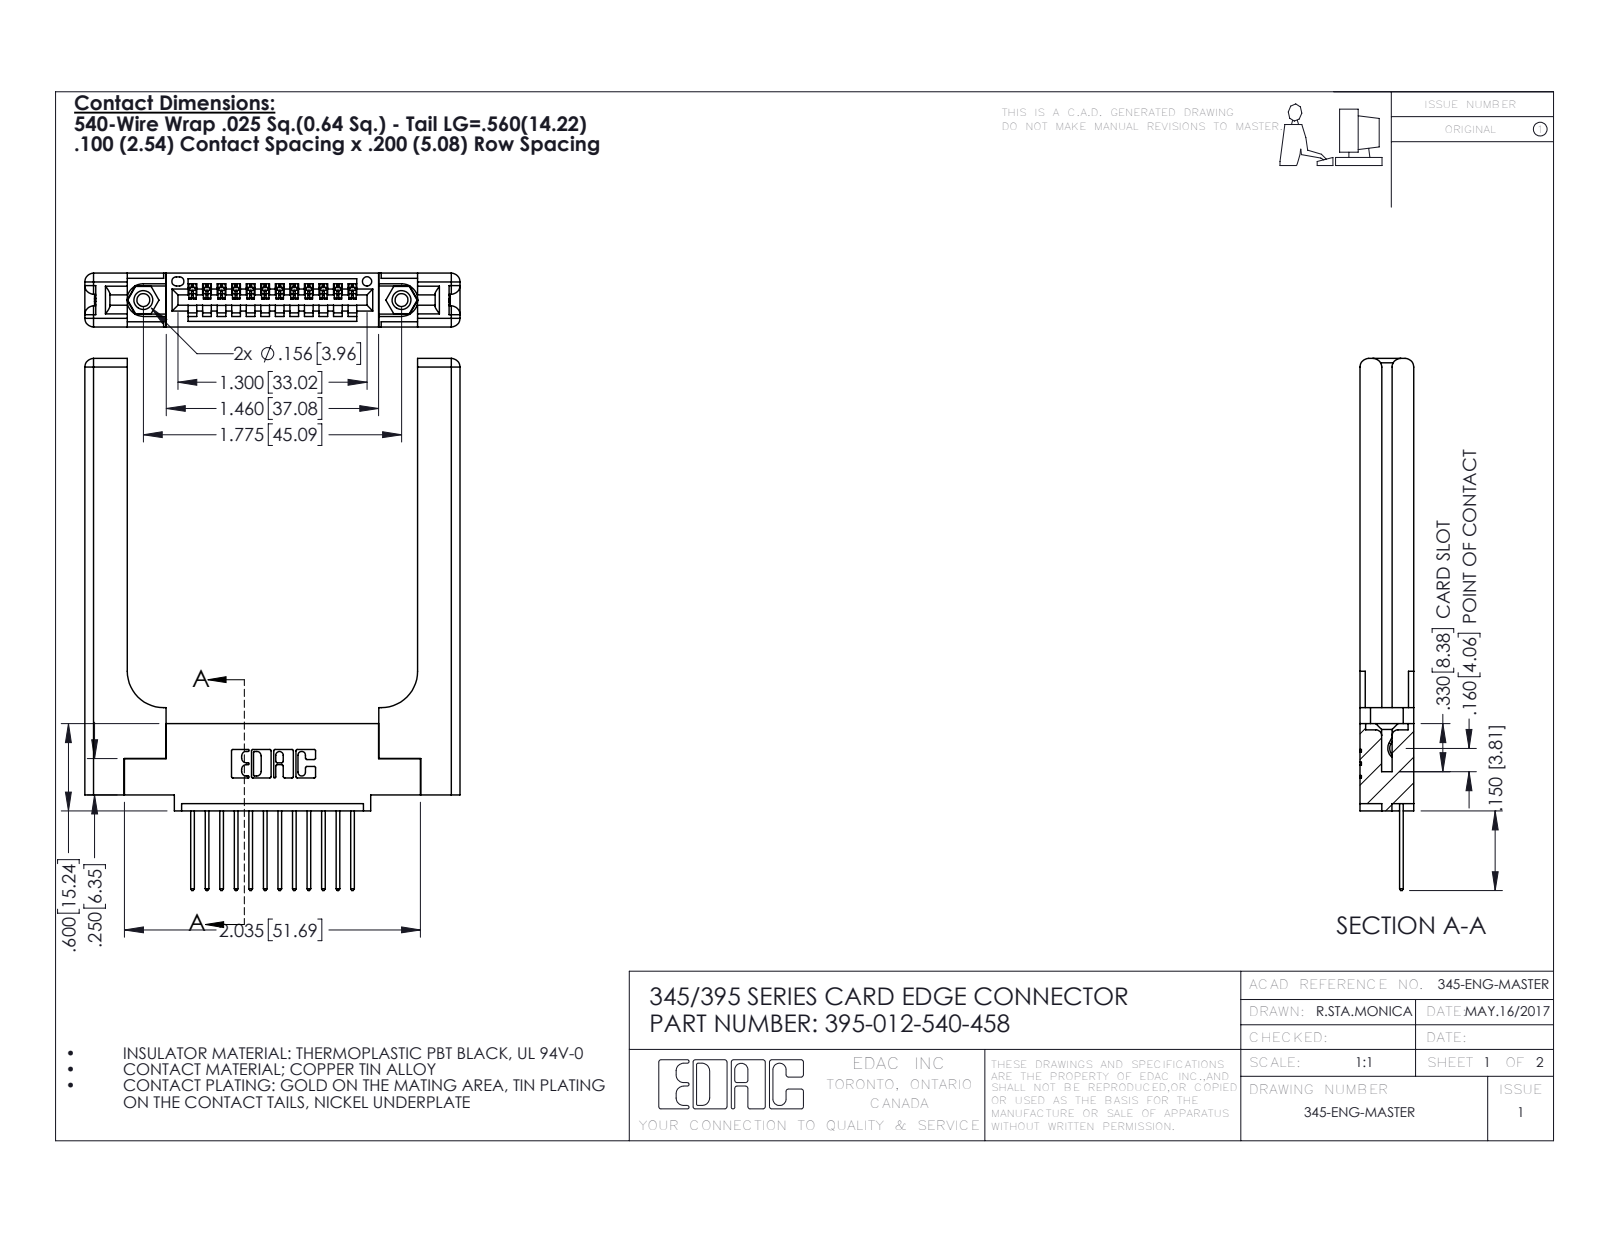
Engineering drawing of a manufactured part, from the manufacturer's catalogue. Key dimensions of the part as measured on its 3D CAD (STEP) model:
Part name (STEP PRODUCT): 345-292-001_345-293-140; 345-250-001_345-250-001-102; 345 Part_0.110 Offset - 0.156 Dia-TH; 345-220-058_345-220-058 (+1 more)
STEP written by: SolidWorks 2016 (CONFIG_CONTROL_DESIGN)
Units: inches
Bodies: 17 solids, 1082 faces (712 planar, 310 cylindrical, 60 other)
Overall size (bounding box): 3.657 × 2.579 × 0.37
Volume: 0.88 in³ · Surface area: 20.09 in²
Round holes (diameter × count): ⌀0.089 ×2, ⌀0.125 ×2, ⌀0.156 ×2, ⌀0.064 ×1
Round bosses / shafts (diameter × count): ⌀0.155 ×2
Partial cylindrical surfaces — rounded edges, fillets, slot ends (radius × count): R0.006 ×24, R0.01 ×24, R0.01 ×22, R0.06 ×16, R0.007 ×6, R0.031 ×6, R0.026 ×3, R0.03 ×2
Main face-to-face distances: 0.37, 0.072, 0.15, 0.298, 0.22, 0.148, 0.077, 1.996, 0.2, 0.098
Hole centre spacings: 0.27, 1.543, 1.775
